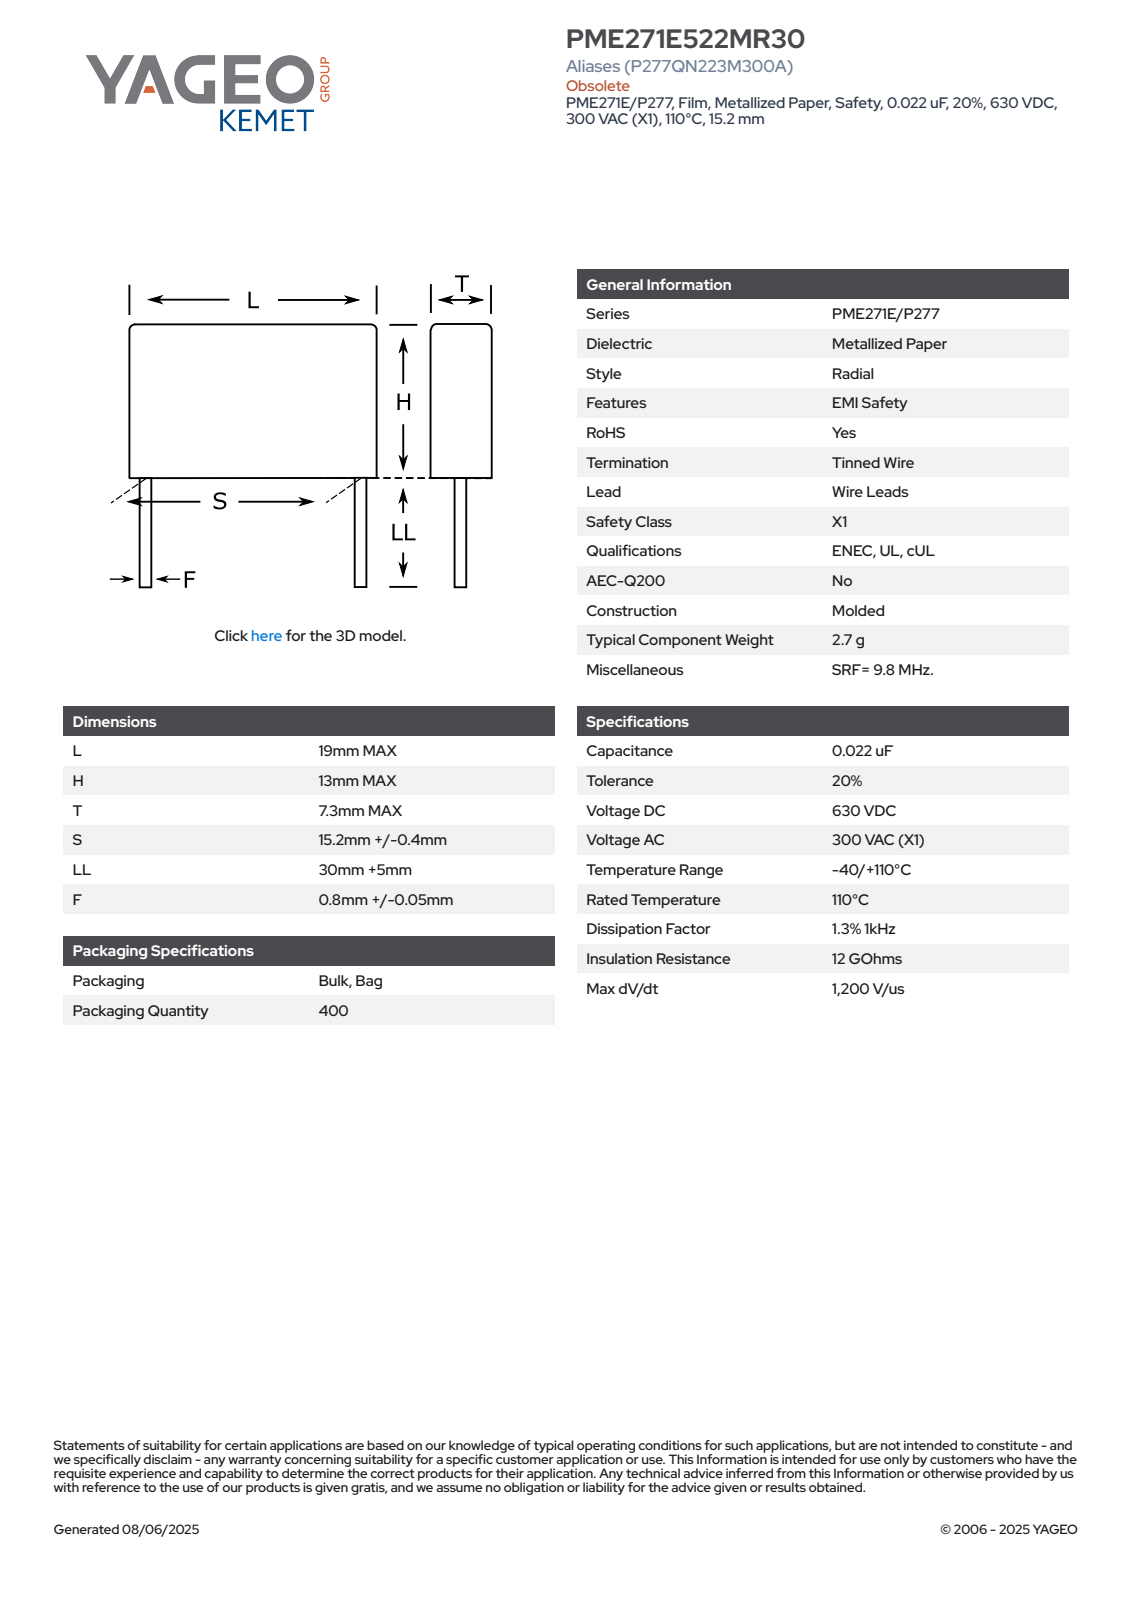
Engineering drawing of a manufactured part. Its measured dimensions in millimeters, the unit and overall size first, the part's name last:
Units: millimetres
Overall size (bounding box): 48 × 19 × 7.3
Round bosses / shafts (diameter × count): ⌀0.85 ×2
Partial cylindrical surfaces — rounded edges, fillets, slot ends (radius × count): R0.5 ×4
Main face-to-face distances: 7.3, 13, 19, 35, 48, 42.15, 7.15, 5.85, 40.45, 5.45
Volume: 1 840 mm³ · Surface area: 1 154 mm²
Bodies: 4 solids, 73 faces (65 planar, 8 cylindrical, 0 other)
Part name (STEP PRODUCT): CFR_MOLDED_19X13X7.3_L19H13T7.3S15.2LL35F0.85
STEP written by: SolidWorks 2014 (AUTOMOTIVE_DESIGN)
